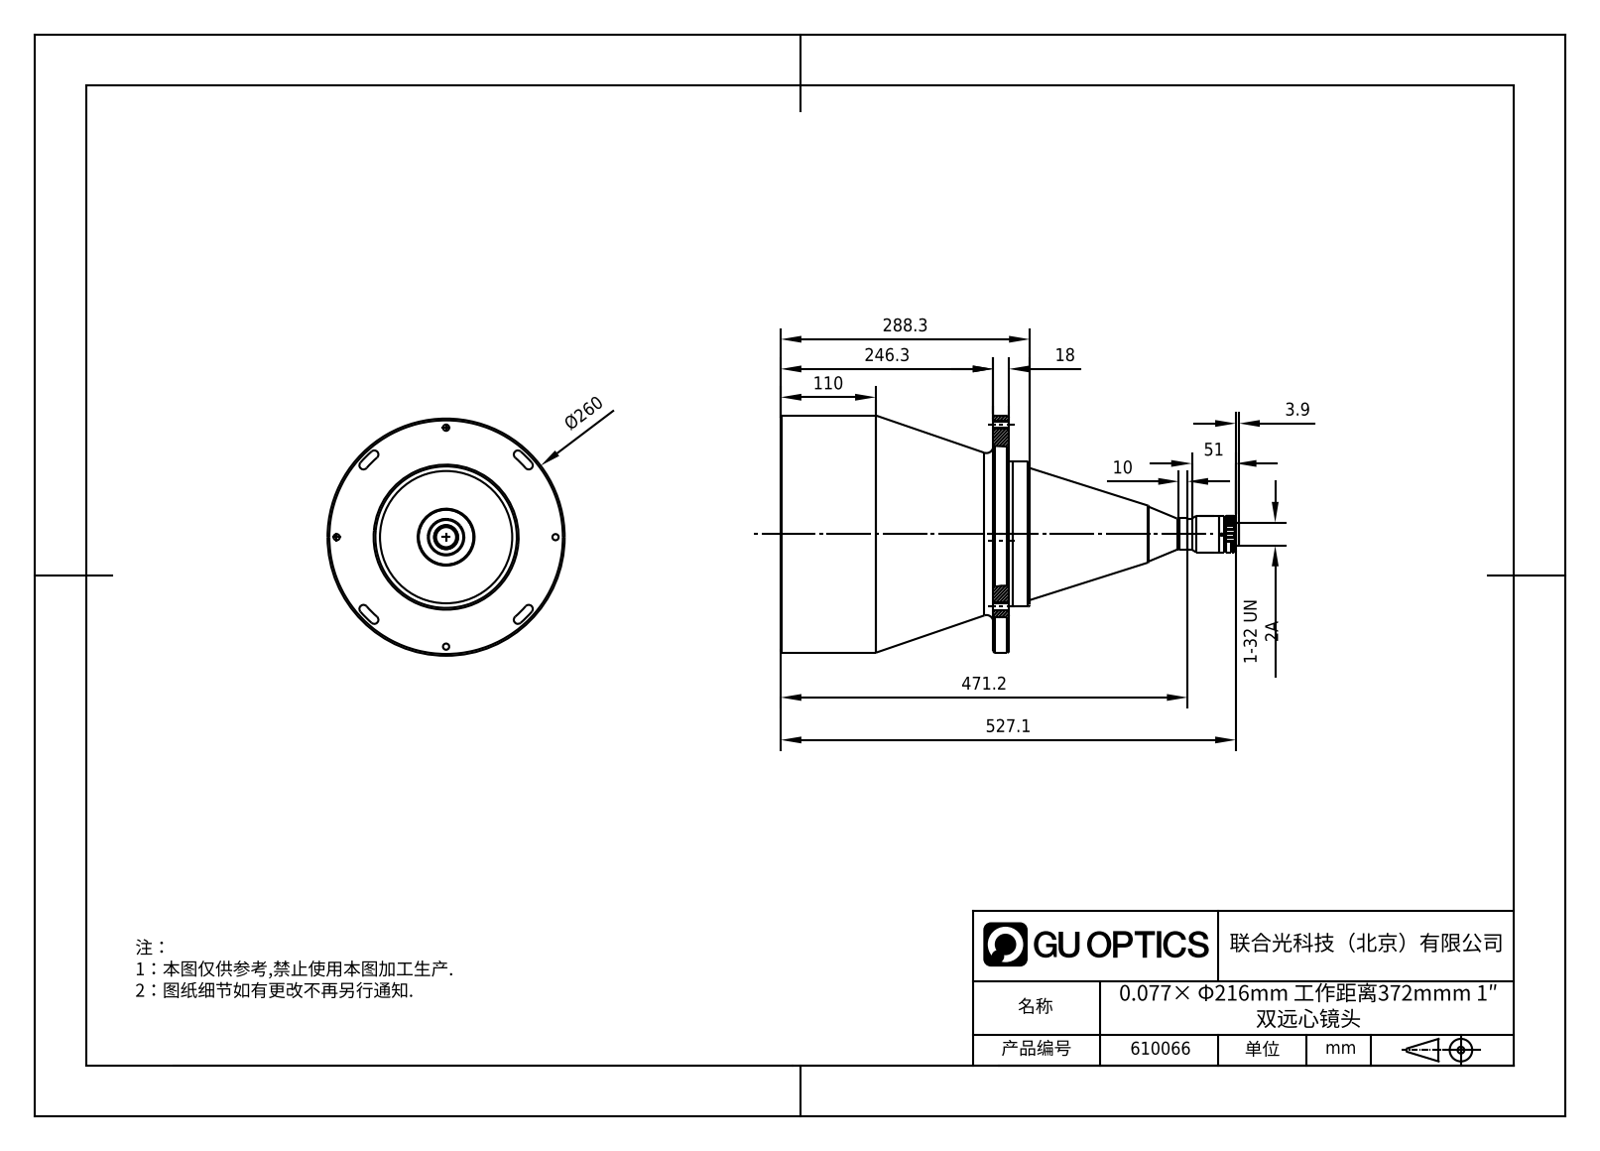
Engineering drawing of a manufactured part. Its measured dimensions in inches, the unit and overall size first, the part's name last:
Units: inches
Overall size (bounding box): 20.907 × 10.236 × 10.236
Round holes (diameter × count): ⌀0.268 ×4, ⌀0.098 ×3, ⌀0.866 ×1, ⌀1.024 ×1, ⌀9.768 ×1
Round bosses / shafts (diameter × count): ⌀10.236 ×1, ⌀6.26 ×1, ⌀5.709 ×1, ⌀1.575 ×1, ⌀1.378 ×1, ⌀1.339 ×1, ⌀1.289 ×1, ⌀1 ×1
Partial cylindrical surfaces — rounded edges, fillets, slot ends (radius × count): R0.118 ×14, R0.177 ×8, R0.157 ×7, R0.085 ×4, R0.04 ×1, R0.055 ×1, R0.094 ×1, R4.547 ×1
Main face-to-face distances: 0.709, 9.697, 10.406, 11.35, 1.654, 0.945, 20.753, 11.056, 10.348, 9.403
Hole centre spacings: 4.724, 6.681, 9.449
Volume: 824.4 in³ · Surface area: 617.8 in²
Bodies: 5 solids, 193 faces (21 planar, 102 cylindrical, 70 other)
Part name (STEP PRODUCT): DTCM110-216-AL
STEP written by: SolidWorks 2017 (CONFIG_CONTROL_DESIGN)
